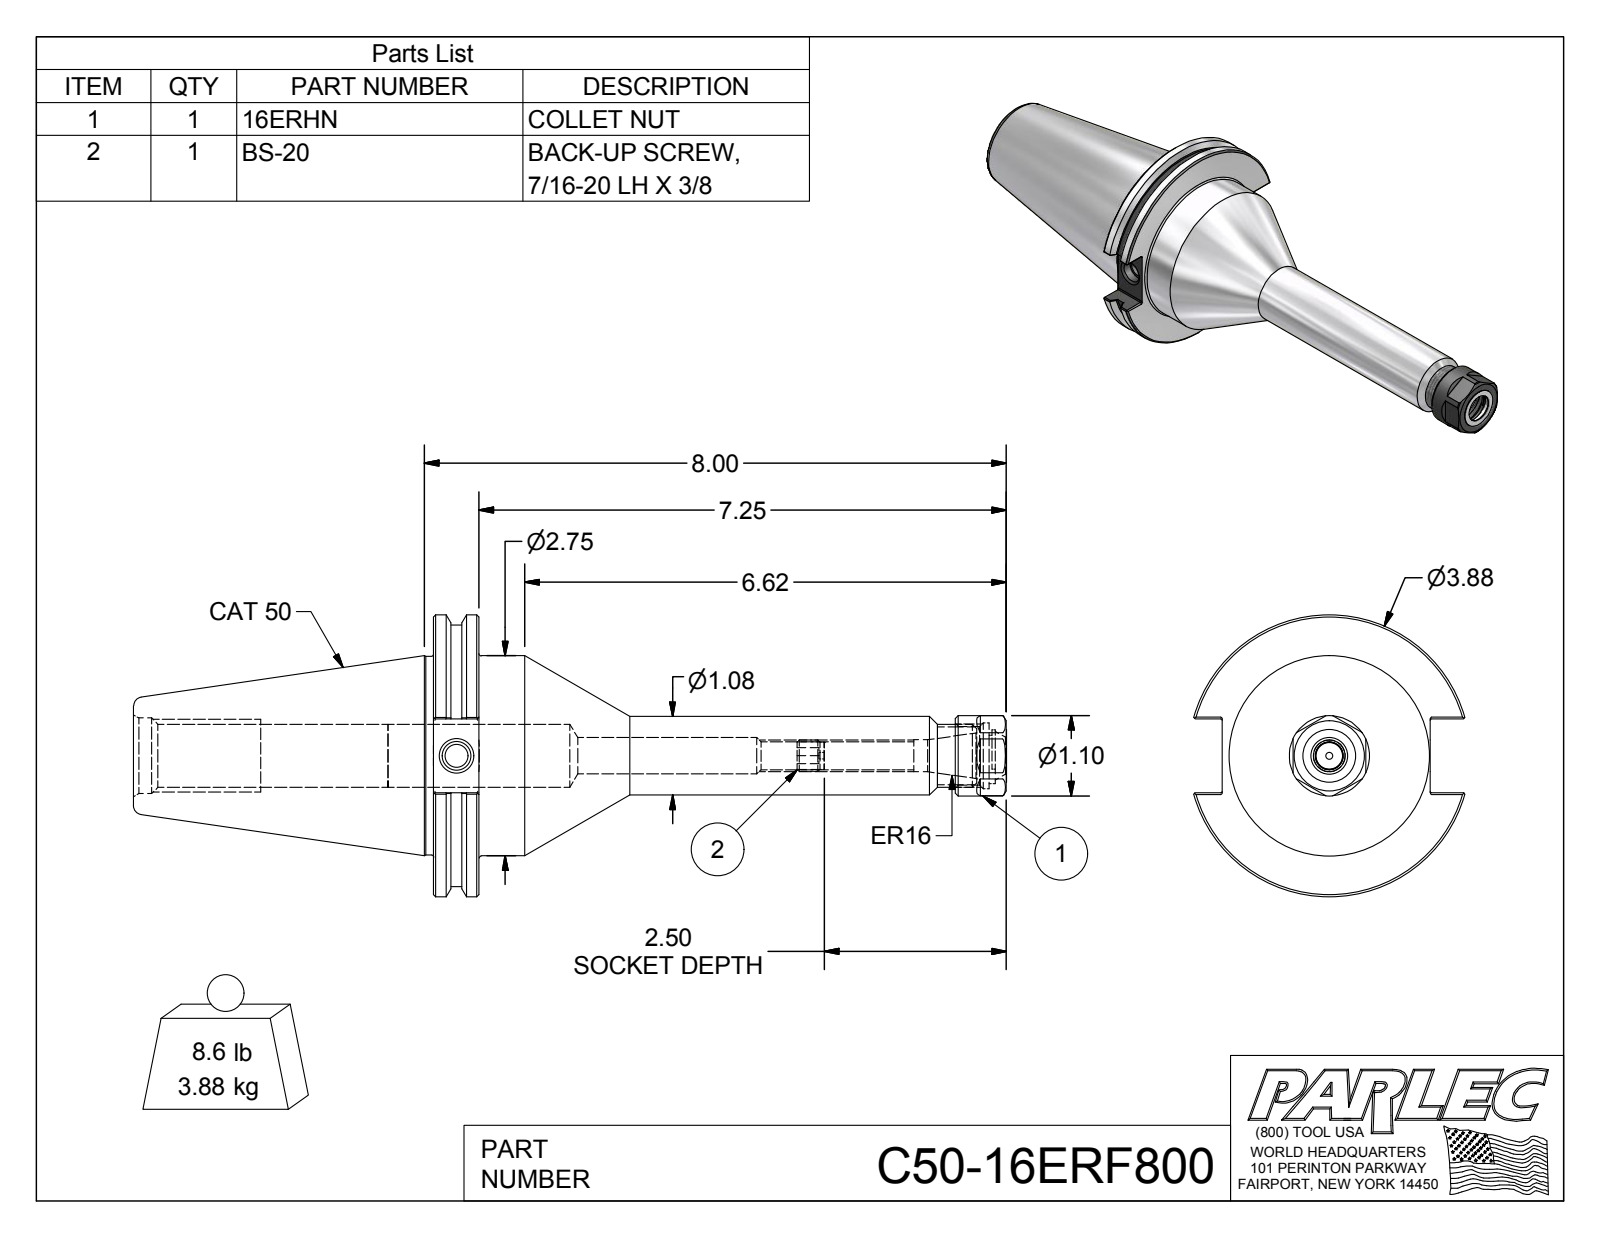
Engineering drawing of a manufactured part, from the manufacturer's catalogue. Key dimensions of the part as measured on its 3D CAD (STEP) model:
Part name (STEP PRODUCT): C50-16ER8-1; 16ERHN; BS-20; C50-16ERF800
STEP written by: Autodesk Inventor 2016 (AUTOMOTIVE_DESIGN)
Units: millimetres
Bodies: 3 solids, 147 faces (59 planar, 40 cylindrical, 48 other)
Overall size (bounding box): 305.1 × 98.42 × 94.71
Volume: 453 042 mm³ · Surface area: 71 555 mm²
Round holes (diameter × count): ⌀2.29 ×1, ⌀8 ×1, ⌀9.73 ×1, ⌀10.13 ×1, ⌀11.18 ×1, ⌀12.4 ×1, ⌀12.7 ×1, ⌀17.02 ×1, ⌀20.5 ×1, ⌀21.95 ×1, ⌀21.97 ×1, ⌀23 ×1
Round bosses / shafts (diameter × count): ⌀98.42 ×1, ⌀91.29 ×1, ⌀69.85 ×1, ⌀69.34 ×1, ⌀28 ×1, ⌀27.43 ×1, ⌀22 ×1, ⌀10.97 ×1
Partial cylindrical surfaces — rounded edges, fillets, slot ends (radius × count): R0.51 ×12, R7.24 ×1, R9 ×1
Main face-to-face distances: 31.88, 15.88, 16, 120.65, 200.33, 184.45, 168.45, 25.14, 104.77, 136.65
Hole centre spacings: 1.52
